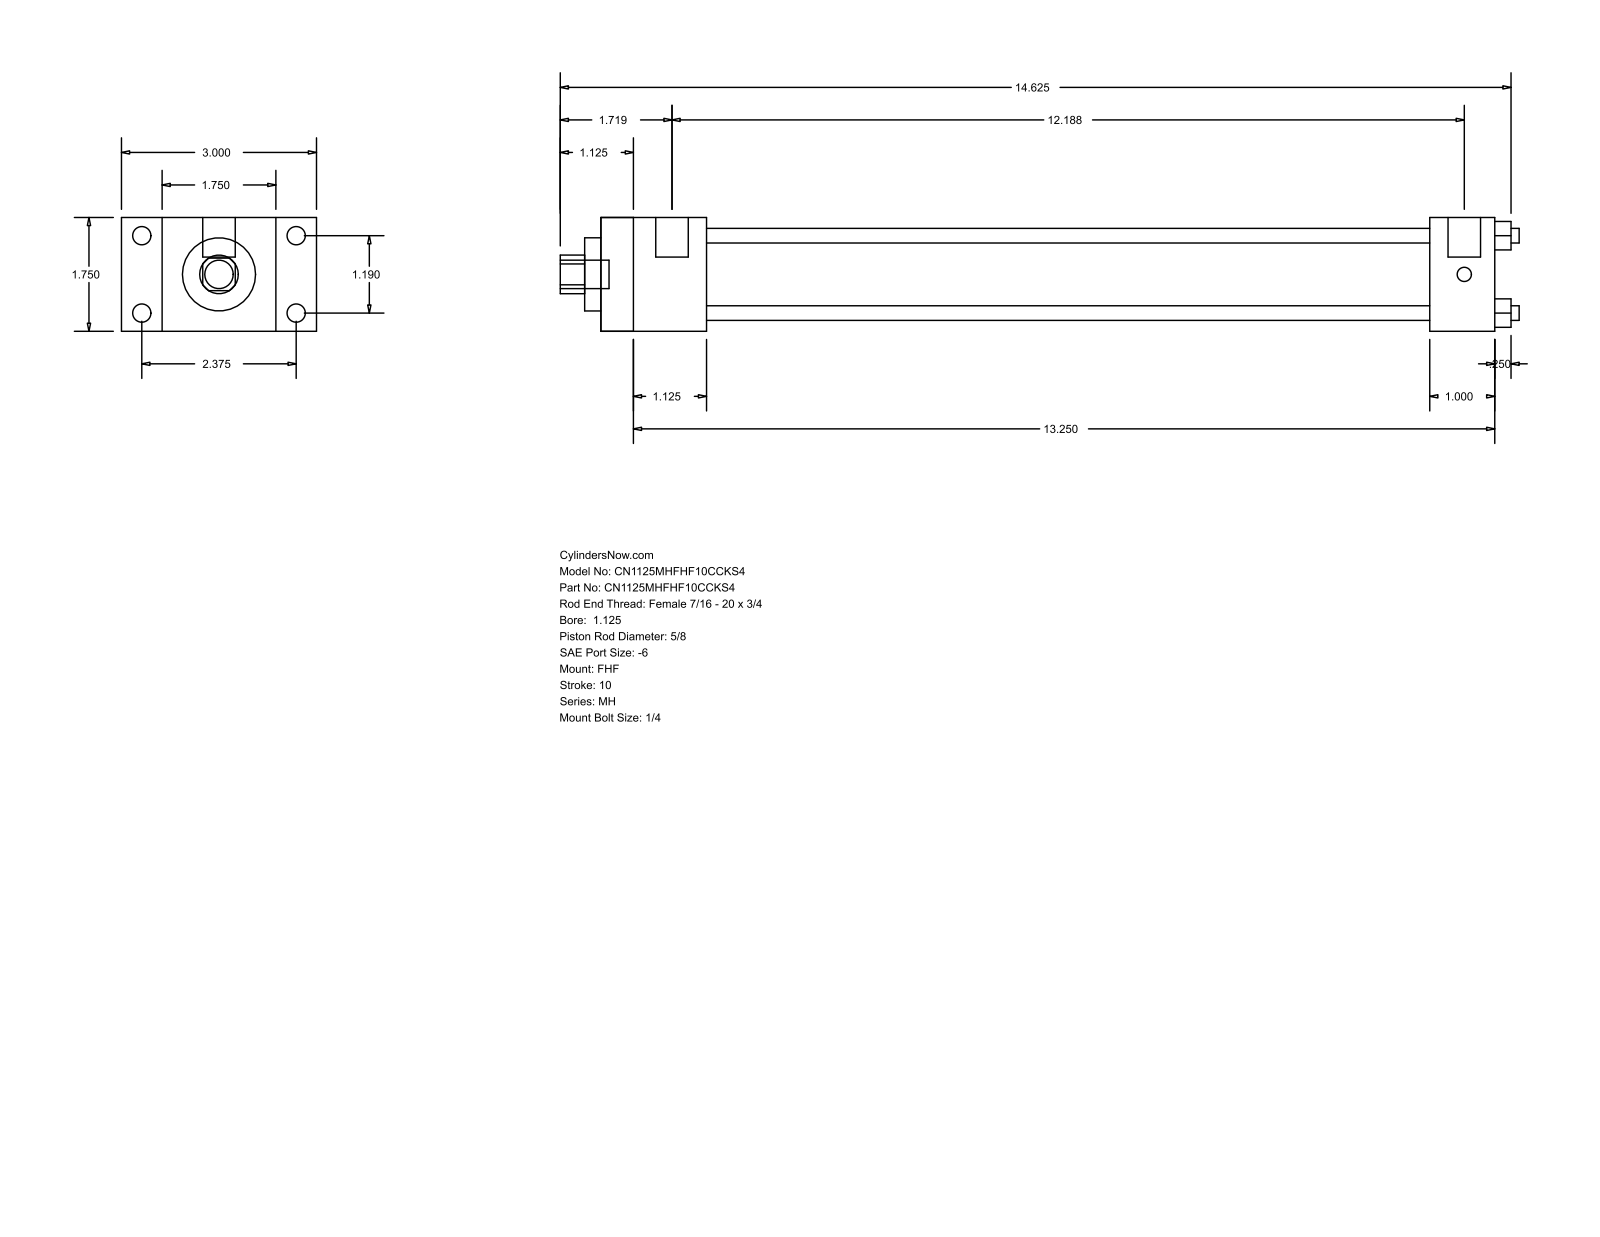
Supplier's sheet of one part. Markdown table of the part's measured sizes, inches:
| quantity | value |
| --- | --- |
| part name | MH_FHF__0112_0.625 |
| STEP written by | GSSL Pune (CONFIG_CONTROL_DESIGN) |
| units | inches |
| bodies | 0 solids, 88 faces (60 planar, 28 cylindrical, 0 other) |
| overall size | 14.75 × 3 × 1.75 |
| round holes (diameter × count) | 0.225 × 4, 0.625 × 1, 1.125 × 1, 1.375 × 1 |
| round bosses / shafts (diameter × count) | 0.281 × 4, 0.219 × 4, 0.5 × 2, 0.437 × 1 |
| partial cylindrical surfaces (radius × count) | 0.297 × 1 |
| main face-to-face distances | 1.75, 0.625, 2.375, 1.625, 3, 13.75, 12.125, 12.75, 11.125, 1 |
| hole center spacings | 0.841, 1.19, 1.683 |
